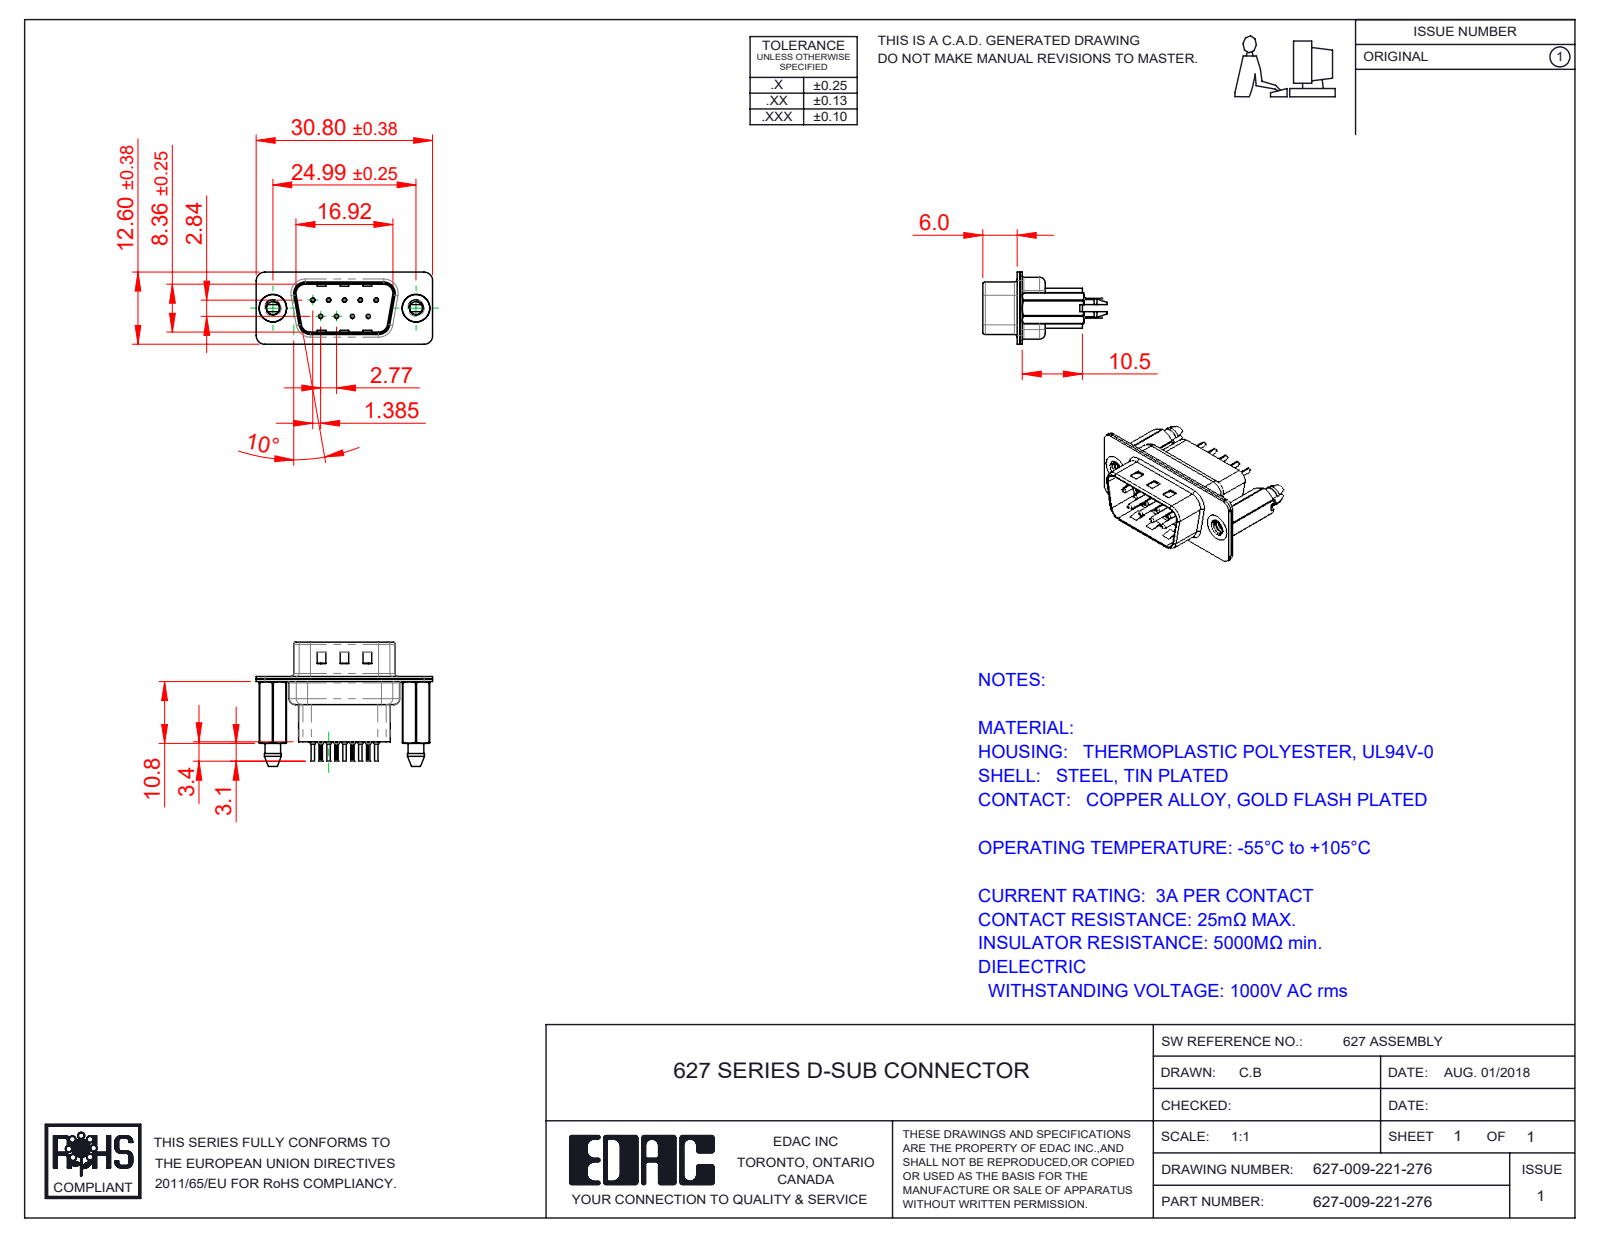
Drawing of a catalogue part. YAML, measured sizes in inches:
part_name: "627 Contact Row 1_21H; 627 Shell Rear_09 Contacts; 627 4-40 Threaded Boardlock_HP; 627 Contact Row 2_21H (+3 more)"
step_written_by: "SolidWorks 2020 (CONFIG_CONTROL_DESIGN)"
units: inches
bodies: {solids: 14, faces: 1300, planar: 355, cylindrical: 530, other: 415}
overall_size: [1.213, 0.854, 0.496]
volume: 0.123
surface_area: 8.186
round_holes:
  - {diameter: 0.008, count: 9}
  - {diameter: 0.014, count: 9}
  - {diameter: 0.043, count: 9}
  - {diameter: 0.063, count: 9}
  - {diameter: 0.089, count: 2}
  - {diameter: 0.157, count: 2}
  - {diameter: 0.189, count: 2}
round_bosses_or_shafts:
  - {diameter: 0.079, count: 9}
  - {diameter: 0.059, count: 9}
  - {diameter: 0.03, count: 9}
  - {diameter: 0.024, count: 9}
  - {diameter: 0.193, count: 2}
partial_cylinders:
  - {radius: 0.059, count: 20}
  - {radius: 0.004, count: 18}
  - {radius: 0.079, count: 12}
  - {radius: 0.063, count: 10}
  - {radius: 0.02, count: 8}
  - {radius: 0.01, count: 4}
  - {radius: 0.024, count: 4}
  - {radius: 0.026, count: 4}
face_to_face_distances: [0.018, 0.016, 0.035, 0.032, 0.377, 0.055, 0.059, 0.027, 0.302, 0.043]
hole_center_spacings: [0.124, 0.109, 0.218, 0.198, 0.198, 0.327, 0.294, 0.295]
